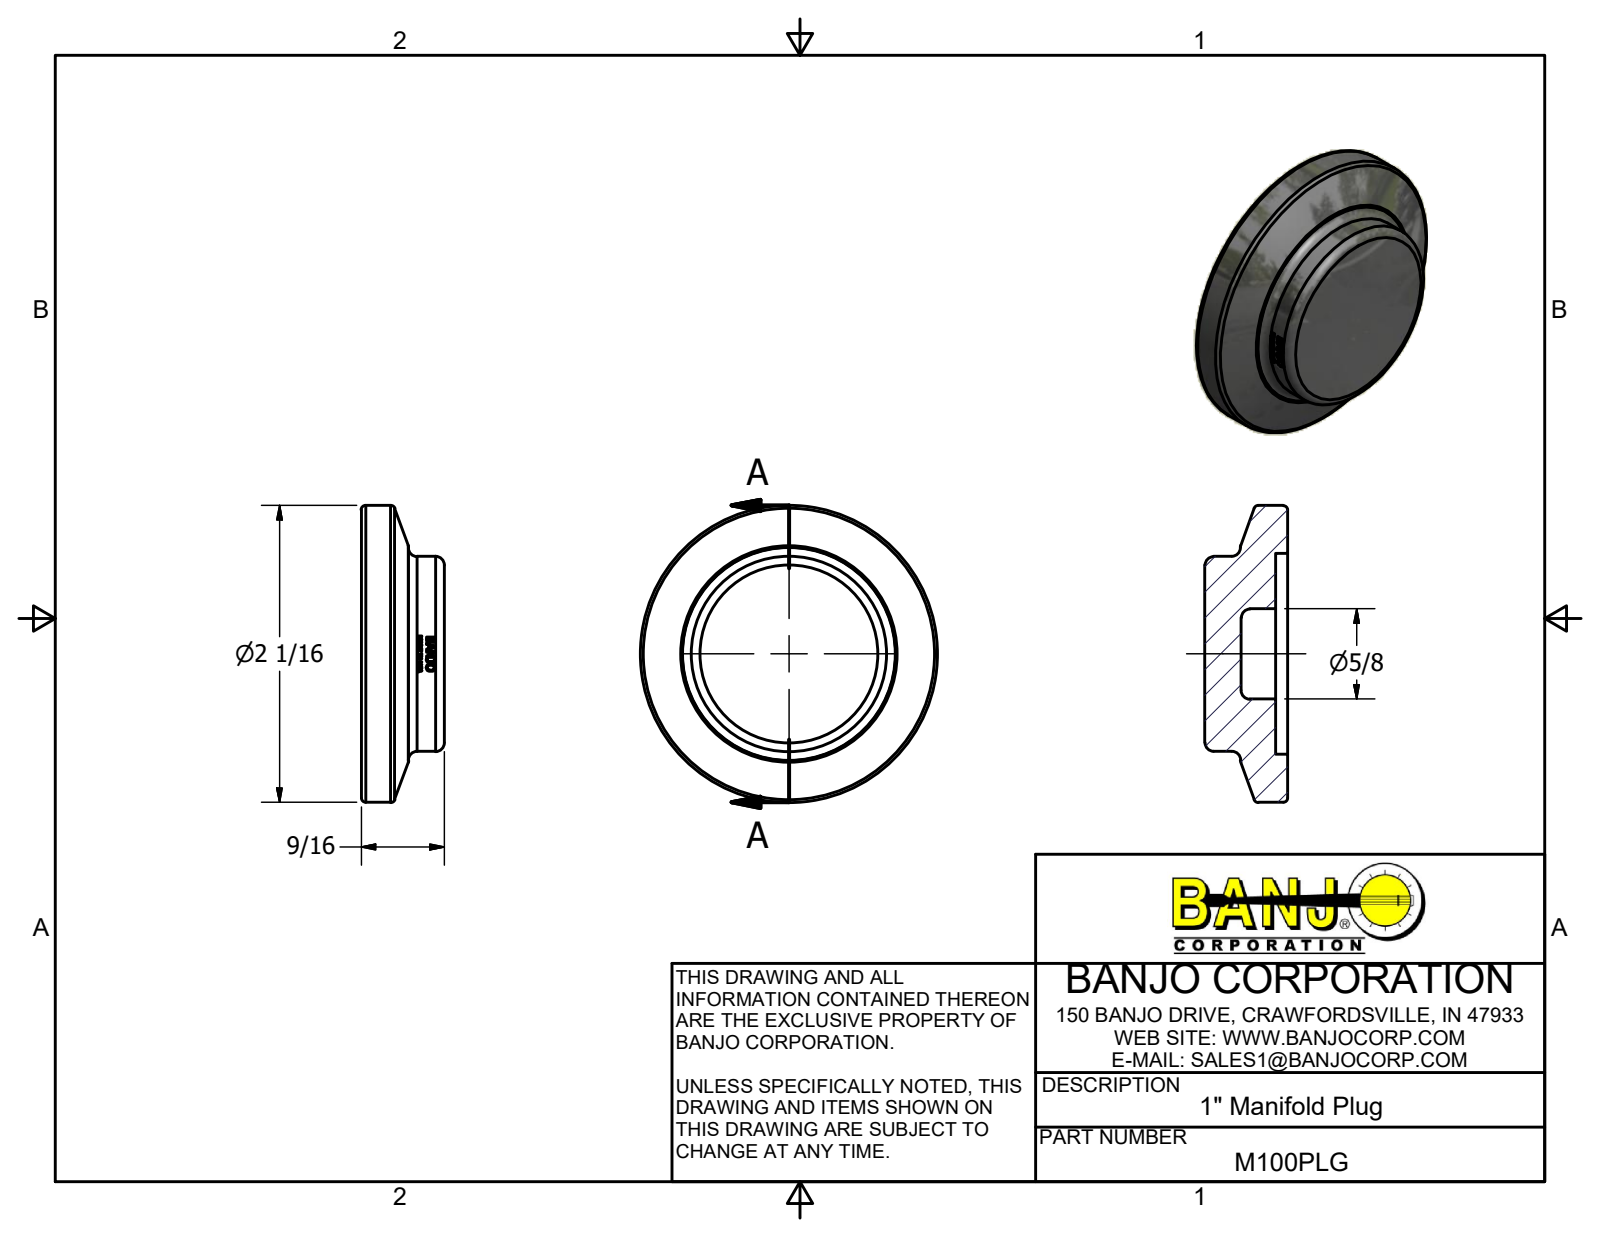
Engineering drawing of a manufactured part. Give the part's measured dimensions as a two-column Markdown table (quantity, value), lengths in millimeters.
| quantity | value |
| --- | --- |
| part name | M100PLG; M100PLGU |
| STEP written by | Autodesk Inventor 2017 (AUTOMOTIVE_DESIGN) |
| units | millimeters |
| bodies | 1 solid, 326 faces (172 planar, 35 cylindrical, 119 other) |
| overall size | 51.82 × 51.82 × 14.48 |
| volume | 18 429 mm³ |
| surface area | 6 286 mm² |
| round holes (diameter × count) | 15.75 × 1, 35.05 × 1 |
| round bosses / shafts (diameter × count) | 51.82 × 1, 34.04 × 1 |
| partial cylindrical surfaces (radius × count) | 16.26 × 1 |
| main face-to-face distances | 2.13, 12.35, 14.48, 6.35, 6, 8.13, 8.24, 6.24, 6.11, 2.31 |
